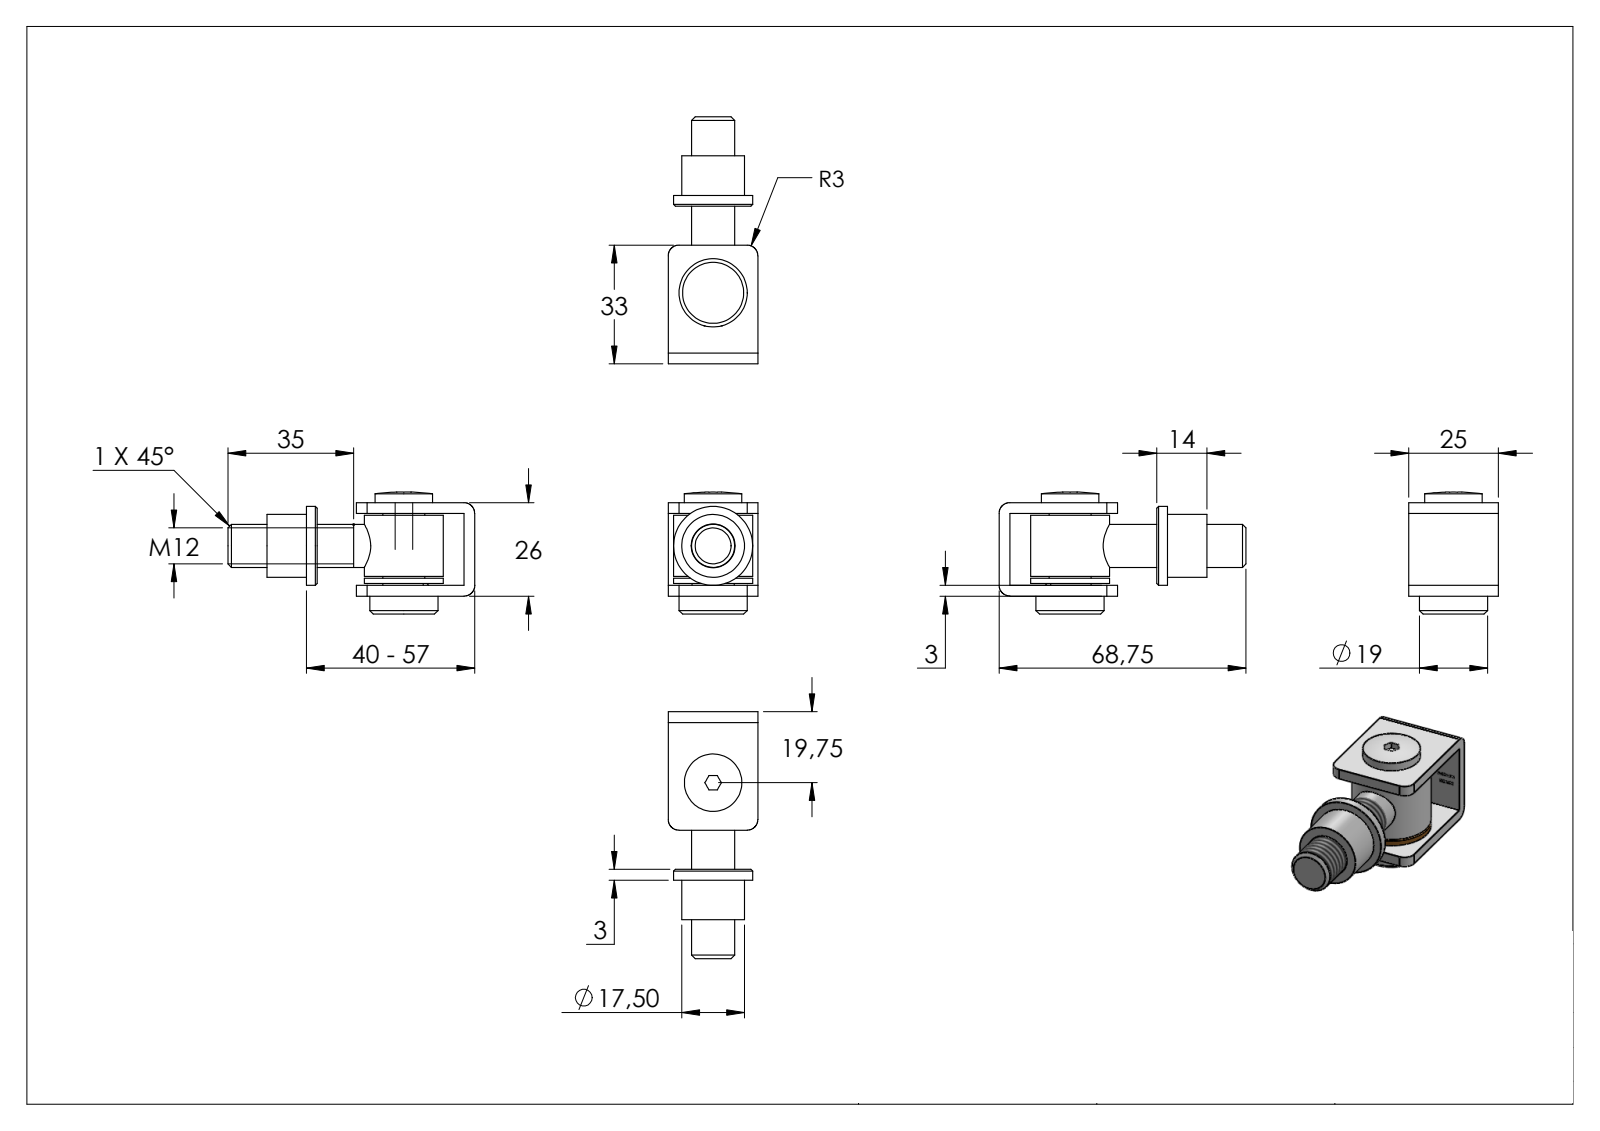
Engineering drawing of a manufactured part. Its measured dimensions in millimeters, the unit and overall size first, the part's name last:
Units: millimetres
Overall size (bounding box): 68.75 × 33.97 × 25
Round holes (diameter × count): ⌀5 ×1, ⌀10.2 ×1, ⌀12.5 ×1
Round bosses / shafts (diameter × count): ⌀22 ×2, ⌀19 ×1, ⌀17.5 ×1, ⌀16 ×1, ⌀12 ×1, ⌀11.7 ×1, ⌀6 ×1
Partial cylindrical surfaces — rounded edges, fillets, slot ends (radius × count): R3 ×4
Main face-to-face distances: 3, 23, 0.5, 26, 20, 22.5, 3.5, 2, 19.5, 17.5
Volume: 21 886 mm³ · Surface area: 13 814 mm²
Bodies: 6 solids, 320 faces (175 planar, 36 cylindrical, 109 other)
Part name (STEP PRODUCT): Torband Teil4; 120-M12; Torband Teil3; Torband Teil1_120-M12 Teil1 (+8 more)
STEP written by: SolidWorks 2018 (CONFIG_CONTROL_DESIGN)
